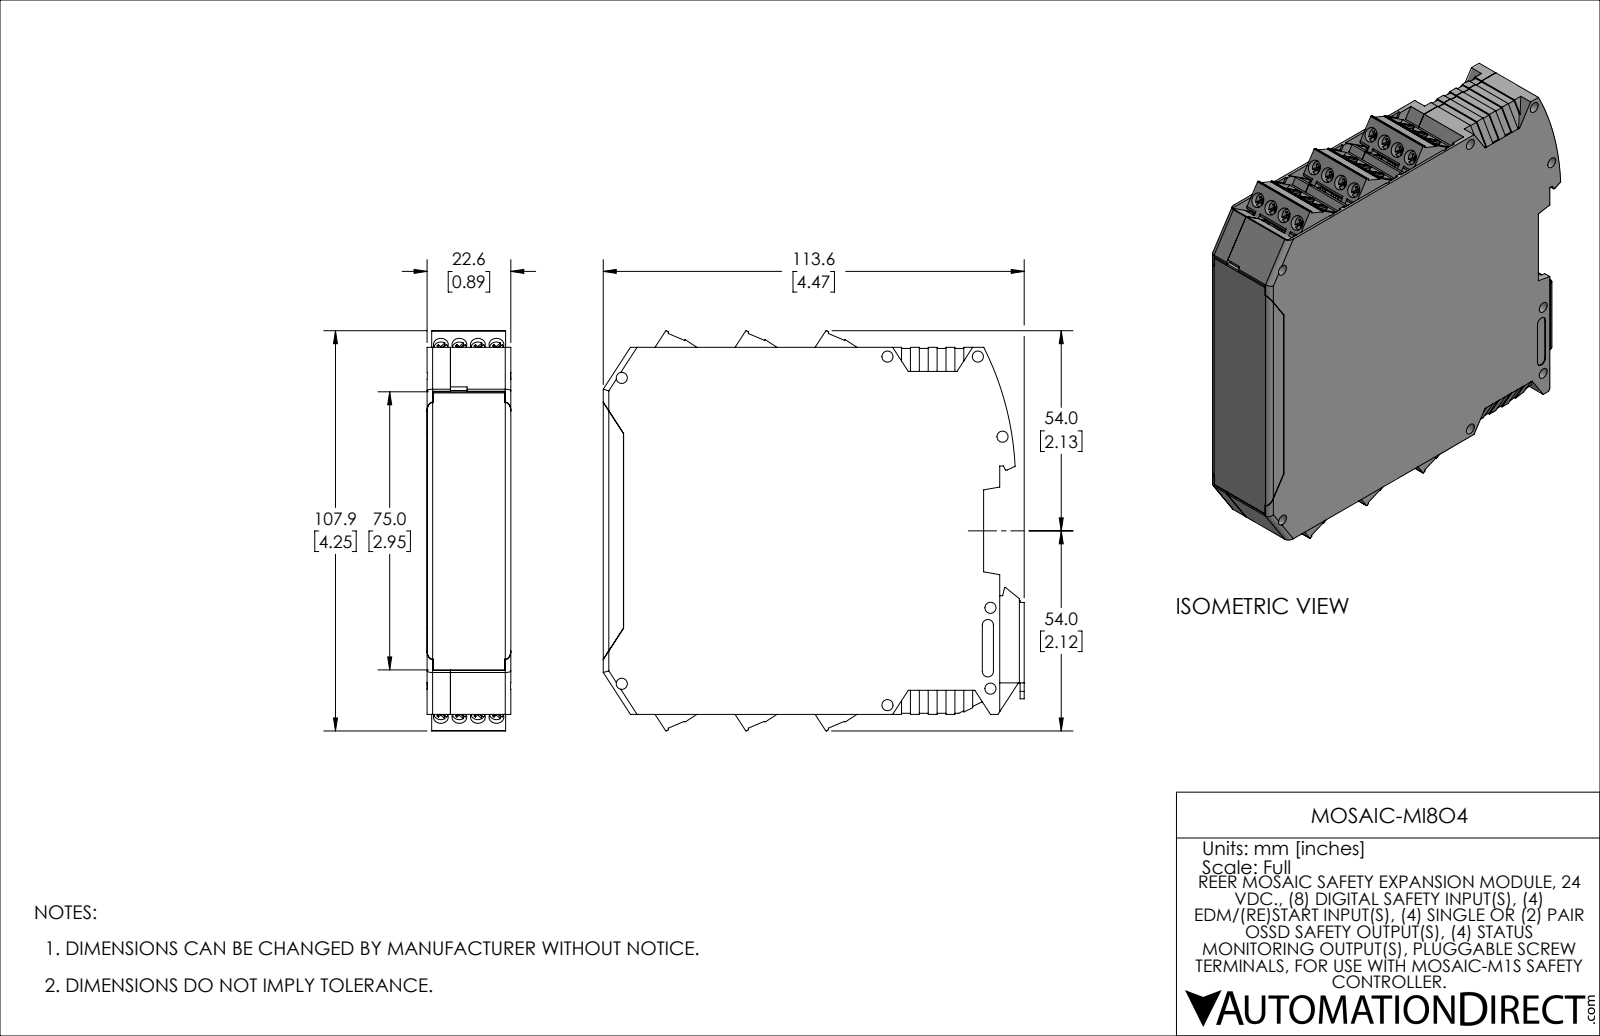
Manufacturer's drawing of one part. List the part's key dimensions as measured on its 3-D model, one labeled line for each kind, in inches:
Part name (STEP PRODUCT): MOSAIC-MI8O4
STEP written by: SolidWorks 2021 (AUTOMOTIVE_DESIGN)
Units: inches
Bodies: 11 solids, 2255 faces (1901 planar, 351 cylindrical, 3 other)
Overall size (bounding box): 4.472 × 4.25 × 0.89
Volume: 3.801 in³ · Surface area: 126.7 in²
Round holes (diameter × count): ⌀0.055 ×26, ⌀0.11 ×24, ⌀0.157 ×24, ⌀0.118 ×14, ⌀0.063 ×1
Round bosses / shafts (diameter × count): ⌀0.149 ×24, ⌀0.177 ×1, ⌀0.11 ×1, ⌀0.053 ×1
Partial cylindrical surfaces — rounded edges, fillets, slot ends (radius × count): R0.012 ×49, R0.114 ×24, R0.008 ×18, R0.03 ×18, R0.059 ×10, R0.024 ×6, R0.039 ×6, R0.098 ×5
Main face-to-face distances: 0.049, 0.841, 0.89, 0.791, 0.197, 0.713, 0.248, 0.039, 0.593, 0.047
Hole centre spacings: 0.197, 0.394, 0.503, 0.504, 0.591, 0.713, 0.74, 0.947
